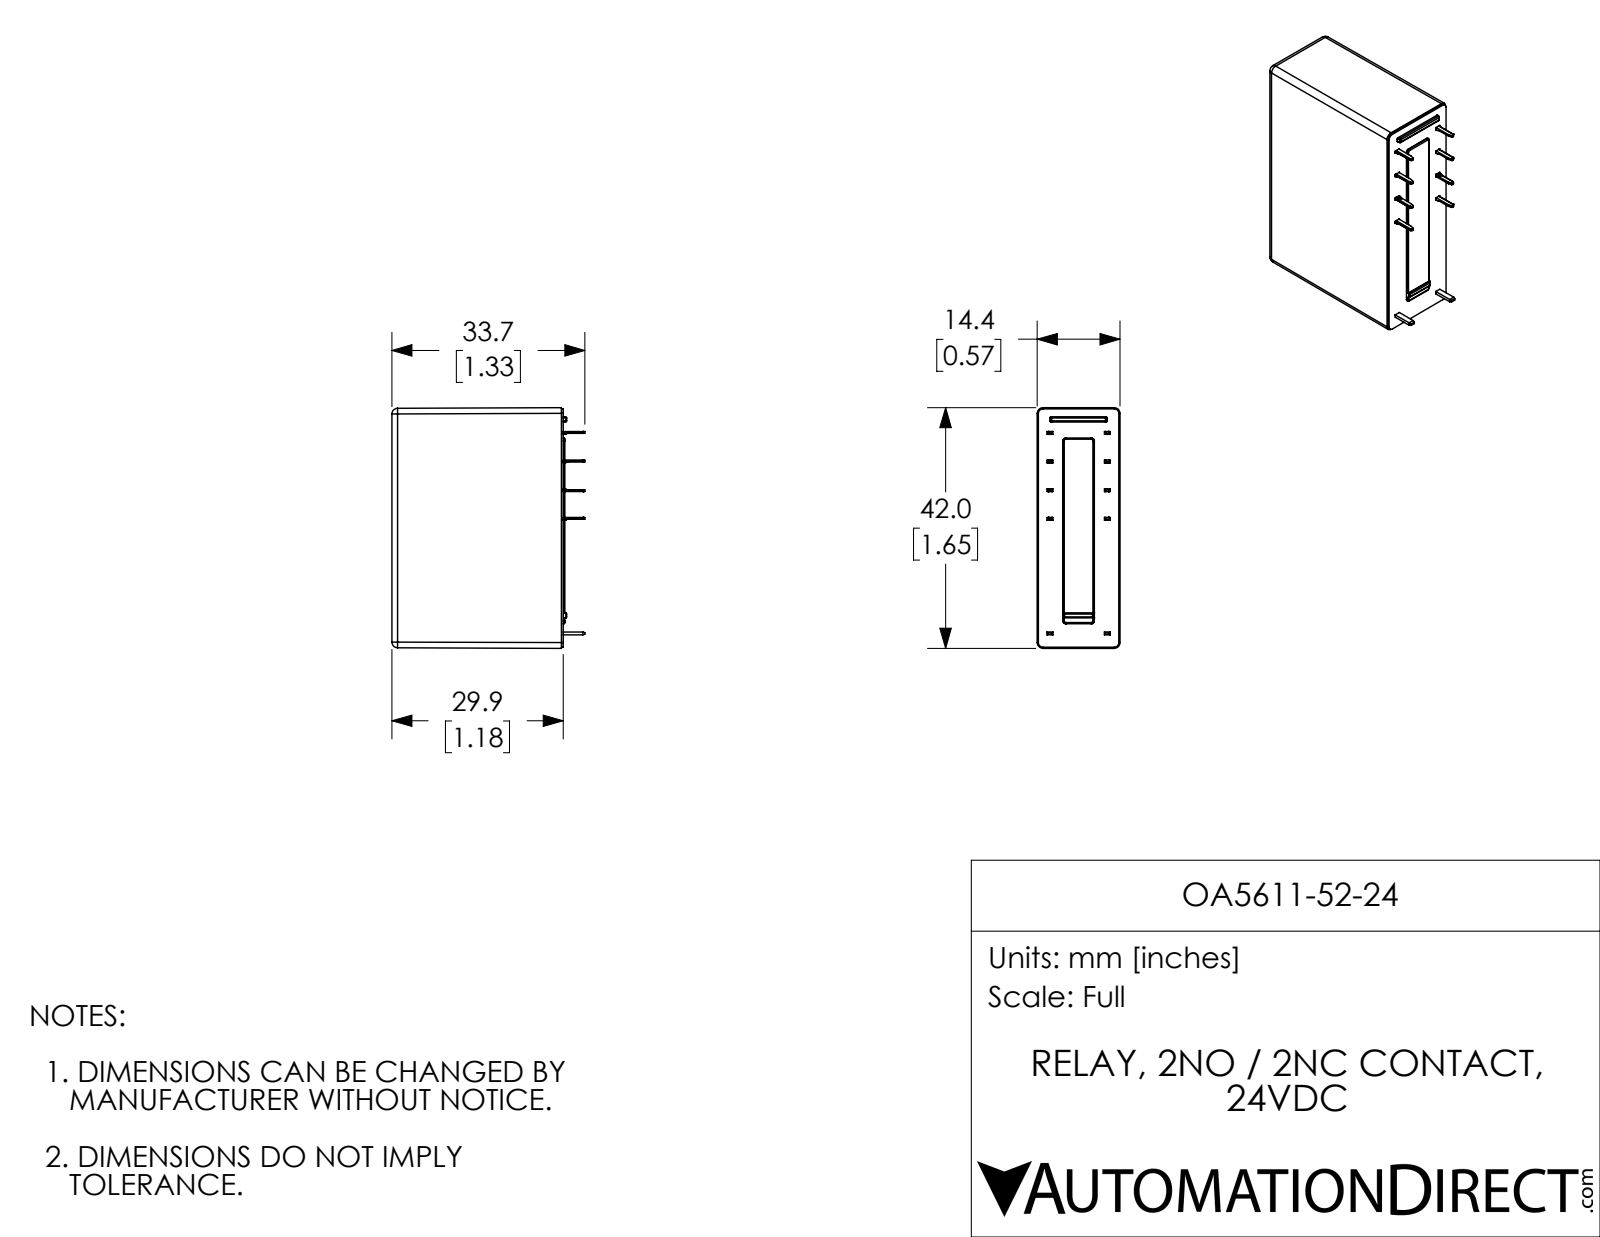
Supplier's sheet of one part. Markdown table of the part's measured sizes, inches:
| quantity | value |
| --- | --- |
| part name | OA5611-52-24 |
| STEP written by | SolidWorks 2017 (AUTOMOTIVE_DESIGN) |
| units | inches |
| bodies | 1 solid, 303 faces (173 planar, 96 cylindrical, 34 other) |
| overall size | 1.653 × 1.327 × 0.569 |
| volume | 1.098 in³ |
| surface area | 7.115 in² |
| round bosses / shafts (diameter × count) | 0.031 × 1 |
| partial cylindrical surfaces (radius × count) | 0.006 × 24, 0.008 × 16, 0.02 × 12, 0.039 × 8, 0.031 × 4, 0.005 × 2, 0.01 × 2 |
| main face-to-face distances | 1.177, 1.189, 0.024, 1.165, 0.035, 0.394, 1.201, 0.554, 0.013, 0.096 |
